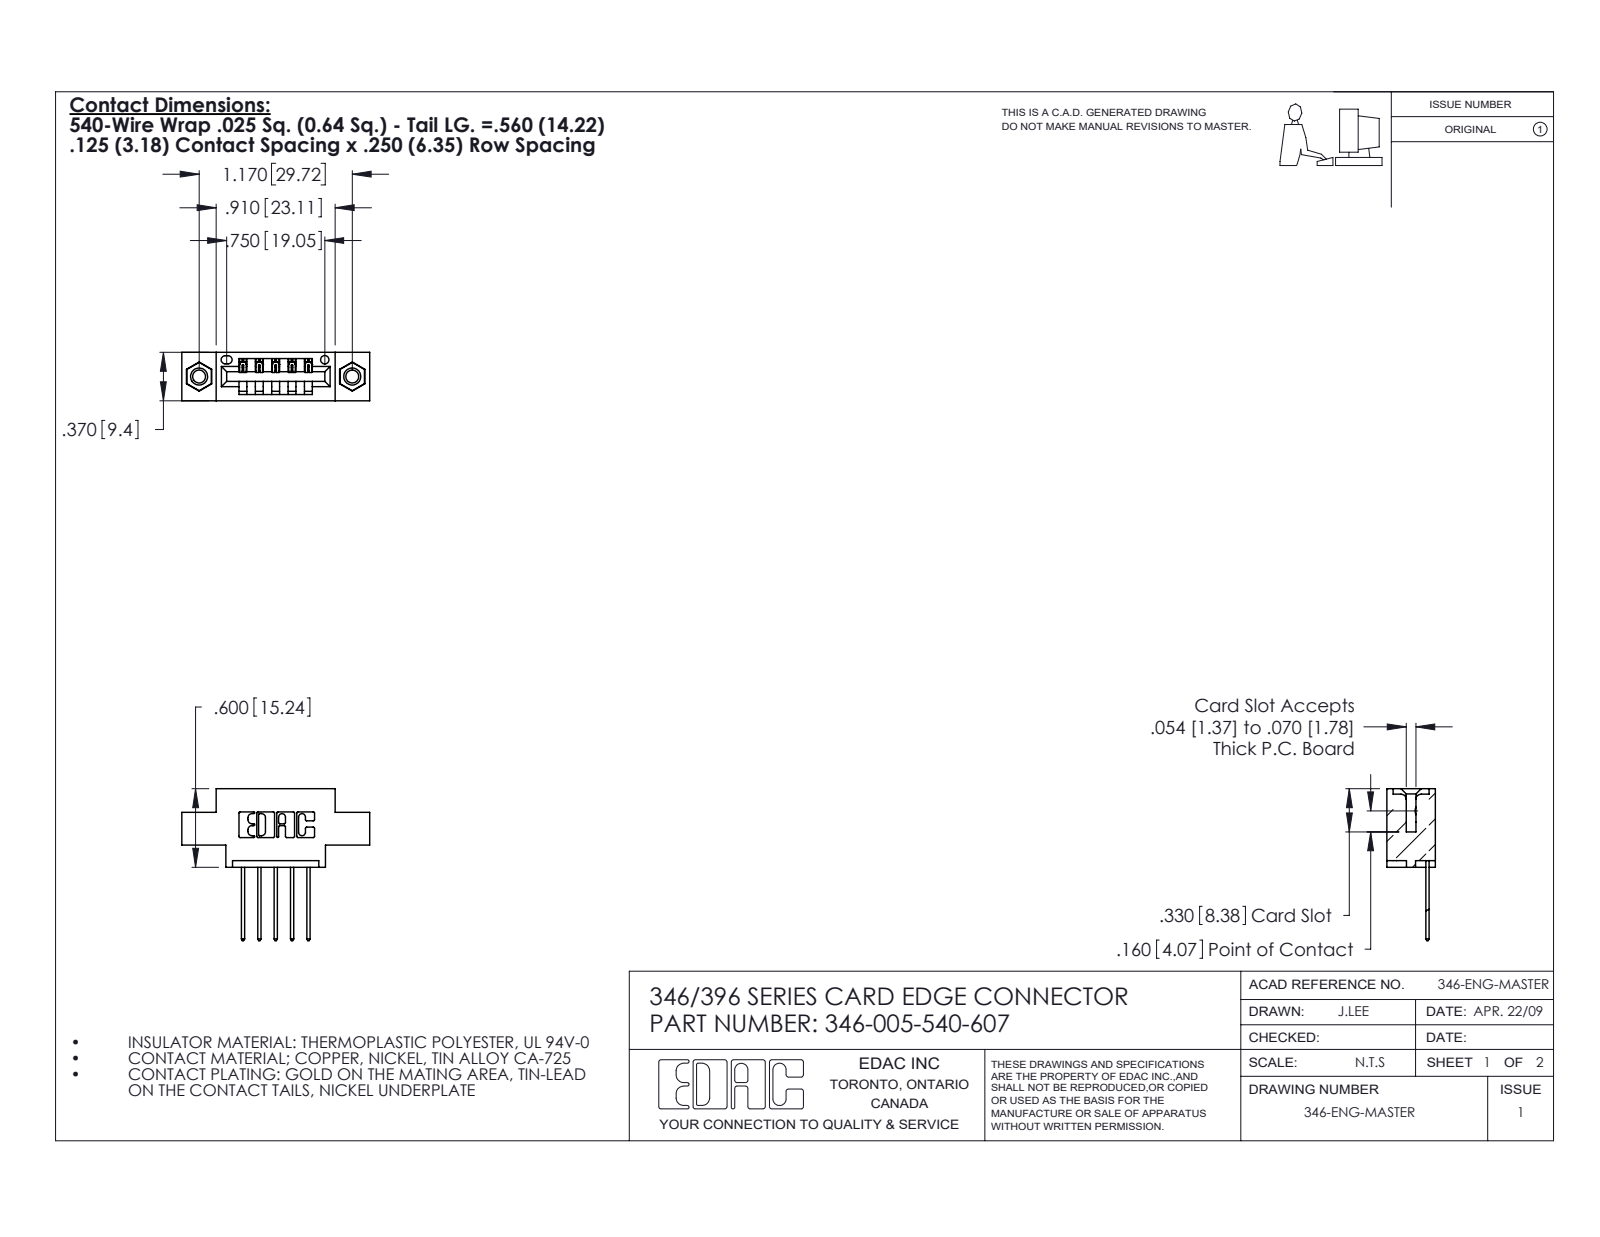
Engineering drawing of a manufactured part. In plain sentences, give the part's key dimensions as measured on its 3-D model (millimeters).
The part is named "345-292-001_345-293-140; 346-005-540-607; 345-250-001_345-250-005-103; 346 Part_0.170 Offset - 0.156 Dia-TI". Its 3-D file was written by "SolidWorks 2020 (CONFIG_CONTROL_DESIGN)". It is 8 solids with 476 faces: 312 planar, 148 cylindrical and 16 other. Overall it measures 36.4 by 29.5 by 9.4 millimeters. Its volume is 3 080 cubic millimeters and its surface area 3 686 square millimeters. Round holes: 2 of diameter 2.5, 2 of diameter 3.2, 2 of diameter 4, 1 of diameter 1.6. Round bosses or shafts: 2 of diameter 3.9. Partial cylindrical surfaces (rounded edges, fillets, slot ends): 22 of radius 0.3, 10 of radius 0.2, 10 of radius 0.3, 6 of radius 0.2, 6 of radius 0.8, 3 of radius 0.7, 2 of radius 0.8, 2 of radius 1. The main face-to-face distances are 6.4, 9.4, 1.2, 8.2, 5.6, 3.8, 1.8, 7.6, 0.6, 2.5. The hole center spacings are 6.2, 24.6, 29.7.
